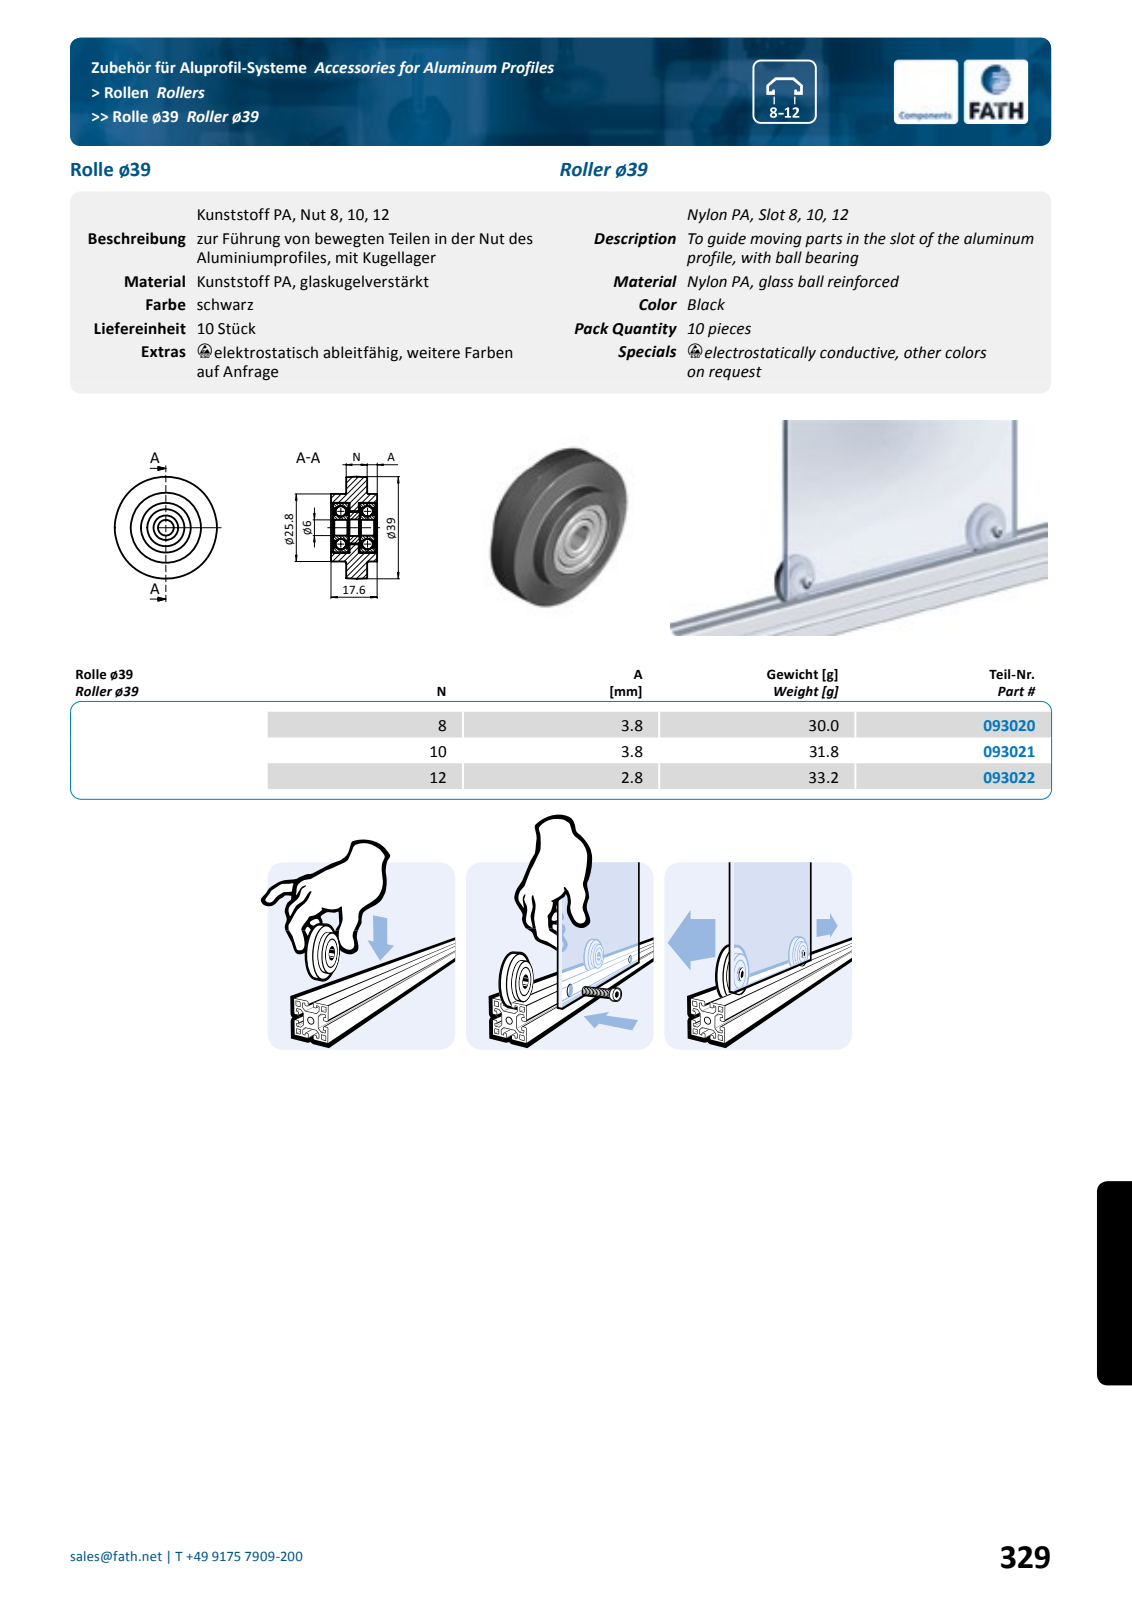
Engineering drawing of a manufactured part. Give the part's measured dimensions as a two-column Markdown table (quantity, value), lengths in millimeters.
| quantity | value |
| --- | --- |
| part name | fath_093020_1; fath_093020_2; fath_093020_3; fath_093020_4 |
| STEP written by | Spatial InterOp 3D (automotive_design) |
| units | millimeters |
| bodies | 4 solids, 94 faces (16 planar, 38 cylindrical, 40 other) |
| overall size | 39 × 39 × 17.6 |
| volume | 13 079 mm³ |
| surface area | 7 622 mm² |
| round holes (diameter × count) | 6 × 1, 6.3 × 1, 12.7 × 1, 15.1 × 1, 19 × 1 |
| round bosses / shafts (diameter × count) | 25.8 × 1, 12 × 1, 9.9 × 1 |
| main face-to-face distances | 8, 6.55, 11.05, 5.25, 6.7, 10.9, 4.35, 0.55, 17.05, 6 |
